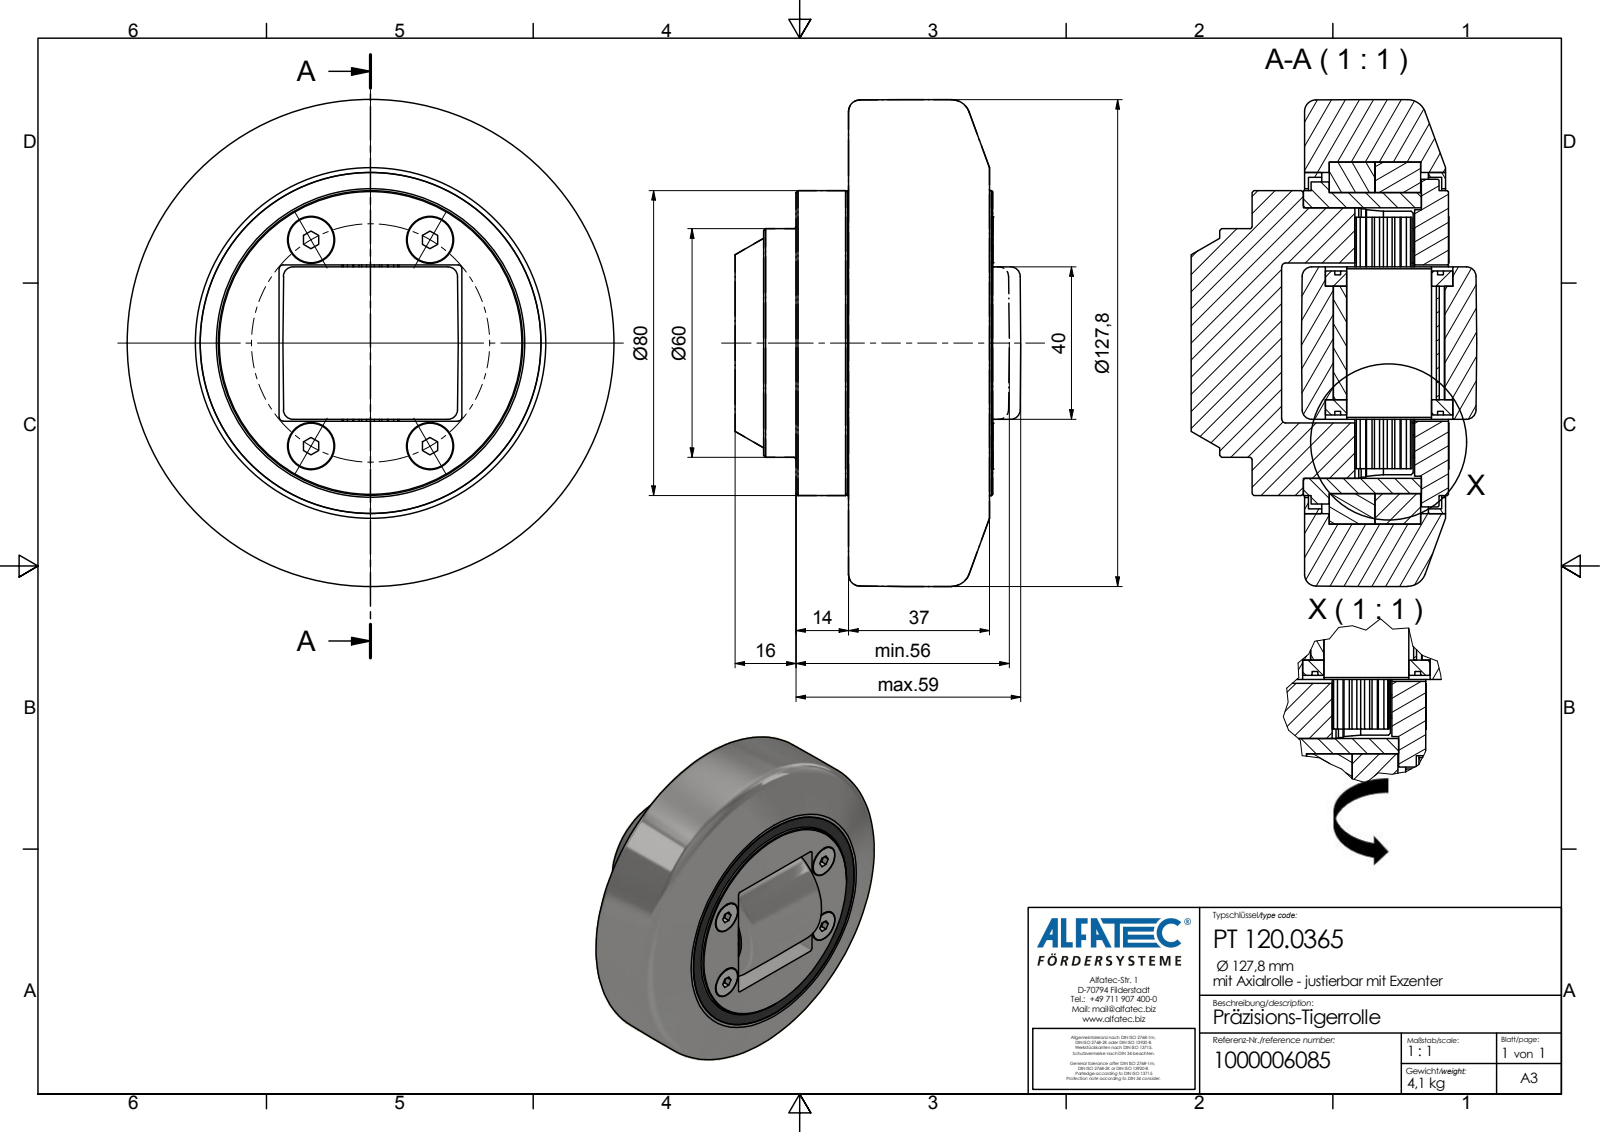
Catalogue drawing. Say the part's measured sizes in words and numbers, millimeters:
The part is named "PT 120.0365_Kontur". Its 3-D file was written by "Autodesk Inventor 2020 (AP242_MANAGED_MODEL_BASED_3D_ENGINEERING_MIM_LF)". It is 1 solid with 66 faces: 41 planar, 8 cylindrical and 17 other. Overall it measures 127.8 by 127.8 by 71.99 millimeters. Its volume is 566 871 cubic millimeters and its surface area 43 543 square millimeters. Round bosses or shafts: 4 of diameter 12, 1 of diameter 80, 1 of diameter 60. The main face-to-face distances are 37.8, 13.8, 51.6, 16, 29.8, 67.6, 66.8, 50.8, 37, 0.8.
